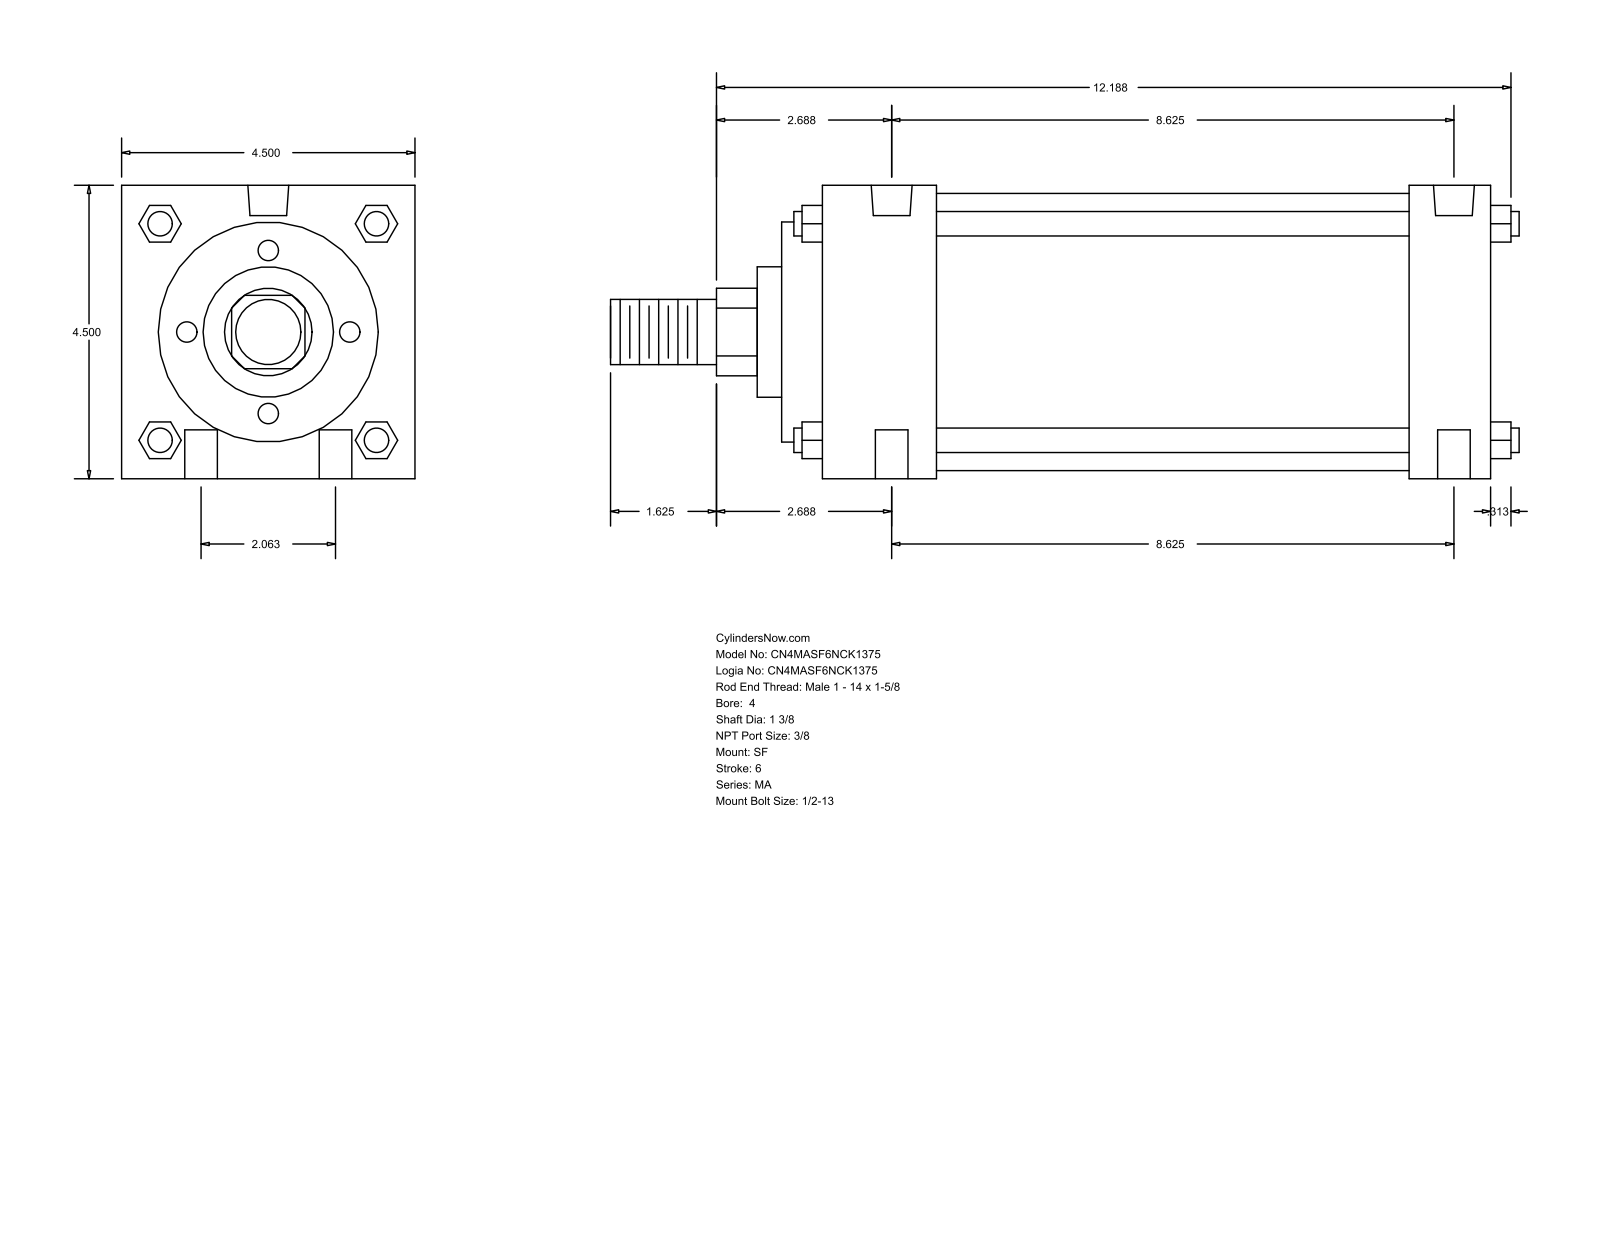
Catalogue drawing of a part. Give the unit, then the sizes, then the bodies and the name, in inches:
Units: inches
Overall size (bounding box): 13.937 × 4.5 × 4.5
Round holes (diameter × count): ⌀0.5 ×4, ⌀0.437 ×2, ⌀0.627 ×2
Round bosses / shafts (diameter × count): ⌀0.375 ×4, ⌀4.25 ×1, ⌀3.375 ×1, ⌀2 ×1, ⌀1.375 ×1, ⌀1 ×1
Partial cylindrical surfaces — rounded edges, fillets, slot ends (radius × count): R0.672 ×1
Main face-to-face distances: 4.5, 10.25, 10.875, 0.625, 9.625, 9, 1.25, 2.375, 1.75, 7.25
Hole centre spacings: 1.031, 8.687, 8.625, 2.062, 8.868, 8.25
Bodies: 0 solids, 126 faces (95 planar, 31 cylindrical, 0 other)
Part name (STEP PRODUCT): MA_SF__0400_1.375
STEP written by: GSSL Pune (CONFIG_CONTROL_DESIGN)
